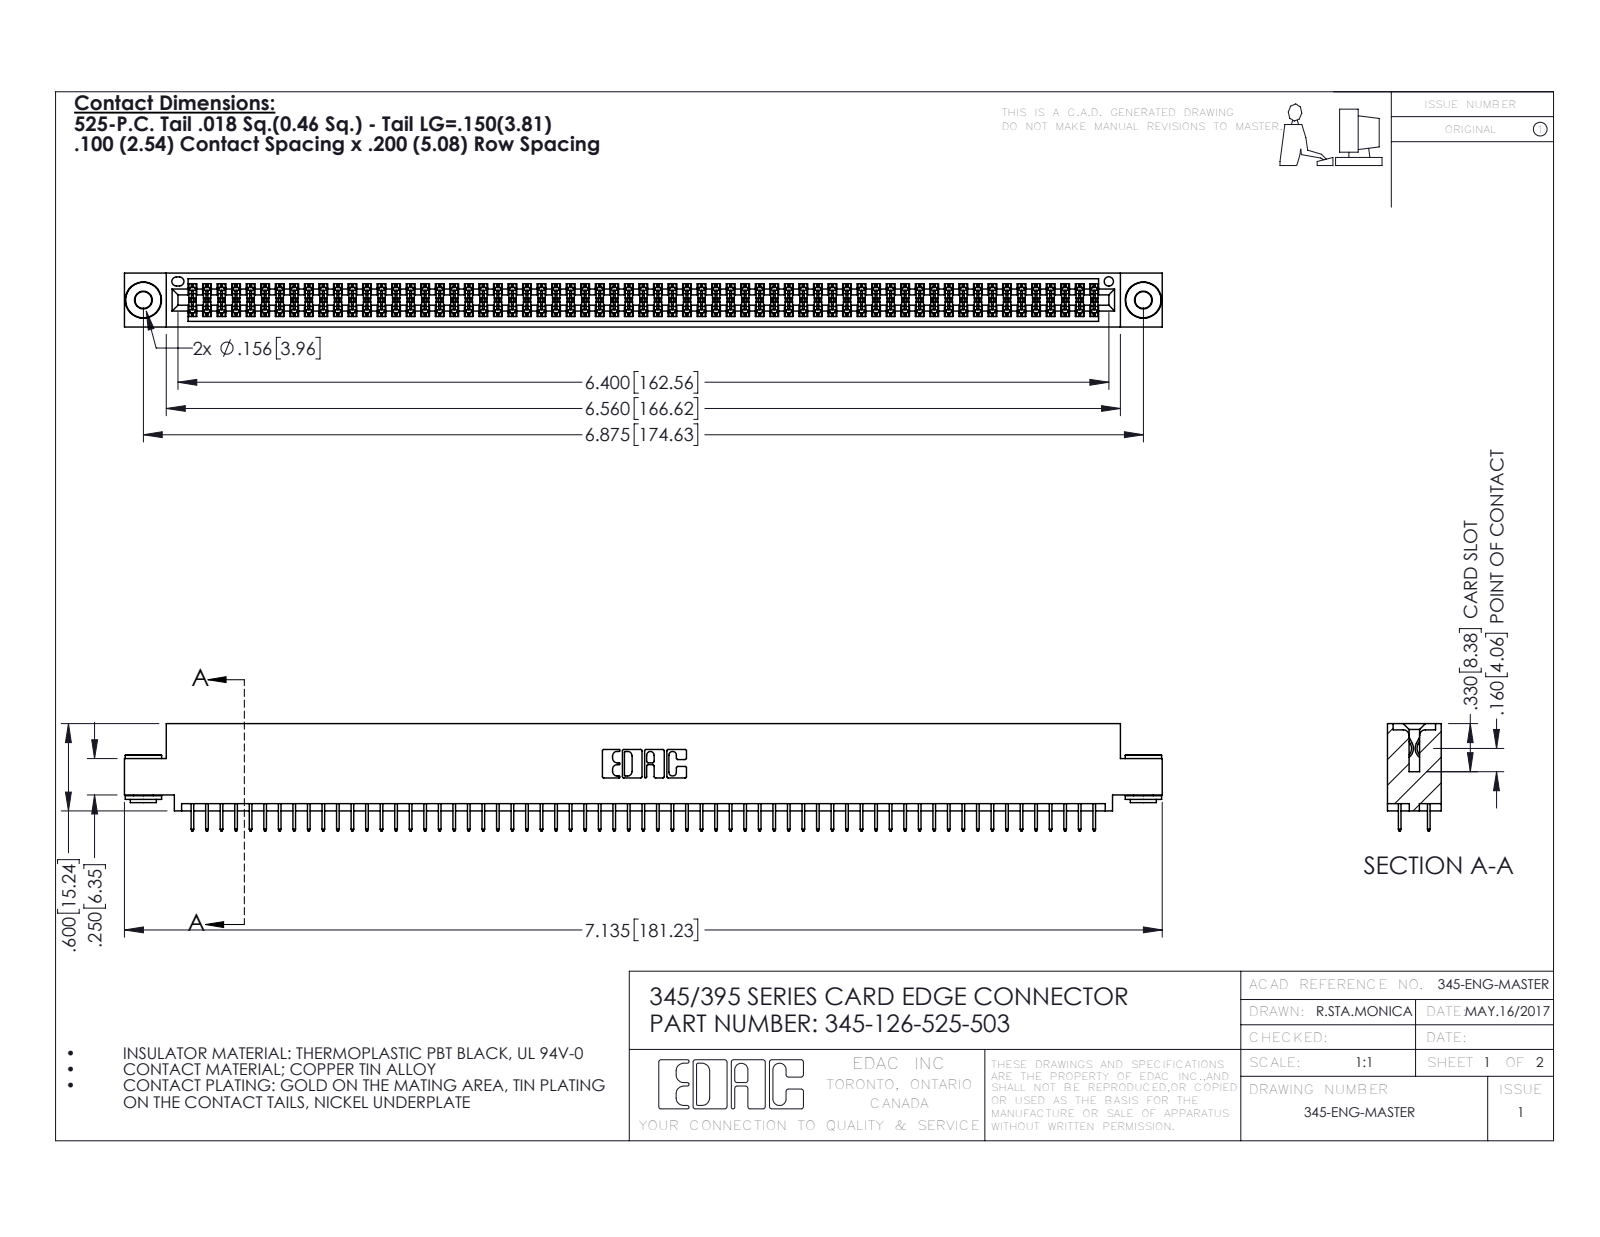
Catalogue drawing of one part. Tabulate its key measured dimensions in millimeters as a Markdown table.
| quantity | value |
| --- | --- |
| part name | 345-292-001_345-293-125; 345-126-525-503; 345 Part_0.110 Offset - 0.156 Dia-TH; 345-250-002_345-250-002-102 |
| STEP written by | SolidWorks 2020 (CONFIG_CONTROL_DESIGN) |
| units | millimeters |
| bodies | 129 solids, 6972 faces (5008 planar, 1956 cylindrical, 8 other) |
| overall size | 181.2 × 18.7 × 9.4 |
| volume | 17 530 mm³ |
| surface area | 26 010 mm² |
| round holes (diameter × count) | 2.9 × 2, 4 × 2, 1.6 × 1 |
| round bosses / shafts (diameter × count) | 6.4 × 2, 4.6 × 2, 3.5 × 2 |
| partial cylindrical surfaces (radius × count) | 0.2 × 252, 0.3 × 22, 0.2 × 6, 0.8 × 6, 0.7 × 3, 0.4 × 2, 0.5 × 2, 0.6 × 2 |
| main face-to-face distances | 1.8, 7.6, 5.1, 9.4, 0.6, 2.5, 6.9, 5.7, 1.8, 4.4 |
| hole center spacings | 6.9, 168.6, 174.6 |
